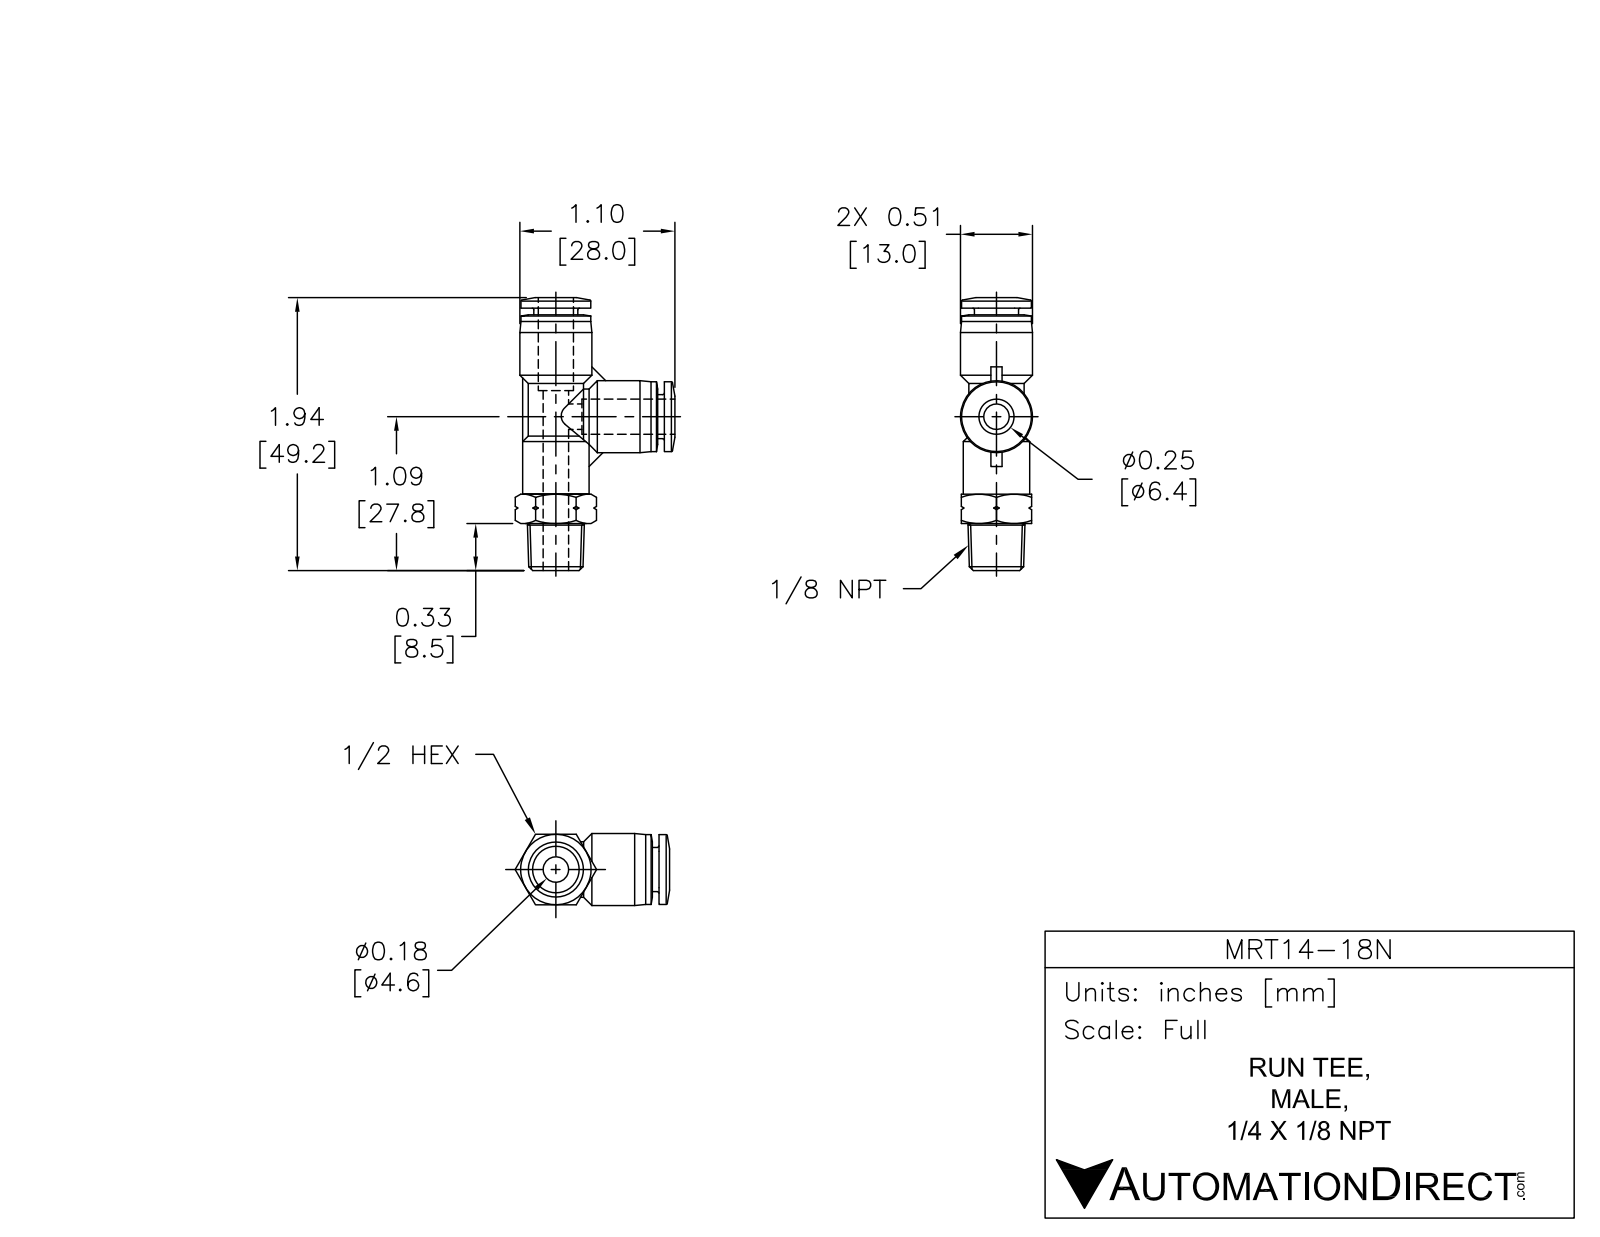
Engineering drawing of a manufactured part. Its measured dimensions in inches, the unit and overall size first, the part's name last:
Units: inches
Overall size (bounding box): 1.941 × 1.135 × 0.512
Round holes (diameter × count): ⌀0.157 ×2, ⌀0.258 ×2
Round bosses / shafts (diameter × count): ⌀0.512 ×2, ⌀0.496 ×2, ⌀0.394 ×2, ⌀0.313 ×2, ⌀0.472 ×1
Main face-to-face distances: 0.5, 0.047, 0.211, 0.289, 1.531, 0.335, 1.866, 0.539, 0.587, 1.819
Volume: 0.343 in³ · Surface area: 6.452 in²
Bodies: 1 solid, 116 faces (23 planar, 31 cylindrical, 62 other)
Part name (STEP PRODUCT): MRT14-18N
STEP written by: SolidWorks 2015 (AUTOMOTIVE_DESIGN)
